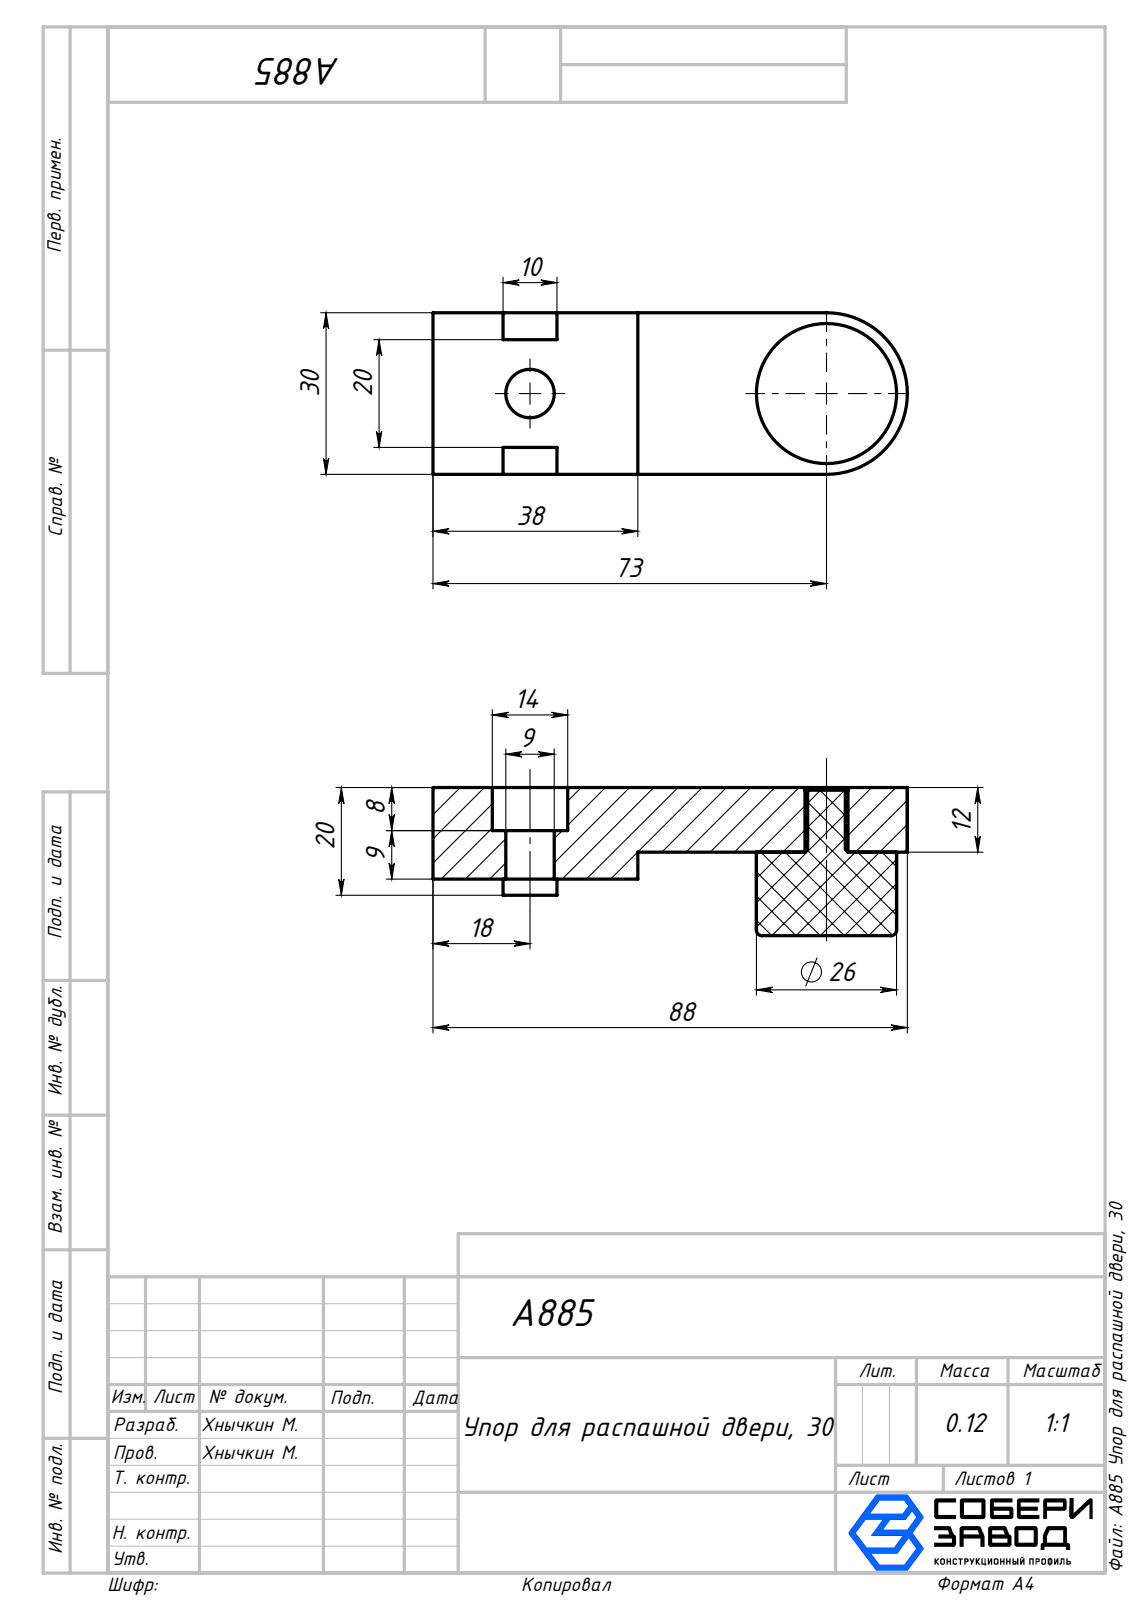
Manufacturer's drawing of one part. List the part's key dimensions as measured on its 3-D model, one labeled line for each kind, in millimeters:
Part name (STEP PRODUCT): A885 Упор для распашной двери, 30; A885 Ножка_00; A885 Корпус_00
STEP written by: SolidWorks 2025 (AUTOMOTIVE_DESIGN)
Units: millimetres
Bodies: 2 solids, 37 faces (19 planar, 12 cylindrical, 6 other)
Overall size (bounding box): 88 × 30 × 27.5
Volume: 43 040 mm³ · Surface area: 11 860 mm²
Round holes (diameter × count): ⌀7 ×1, ⌀9 ×1, ⌀14 ×1
Round bosses / shafts (diameter × count): ⌀26 ×1, ⌀8 ×1
Partial cylindrical surfaces — rounded edges, fillets, slot ends (radius × count): R15 ×1
Main face-to-face distances: 12, 30, 5, 17, 10.5, 15.5, 27.5, 8, 7.5, 38
Hole centre spacings: 55
